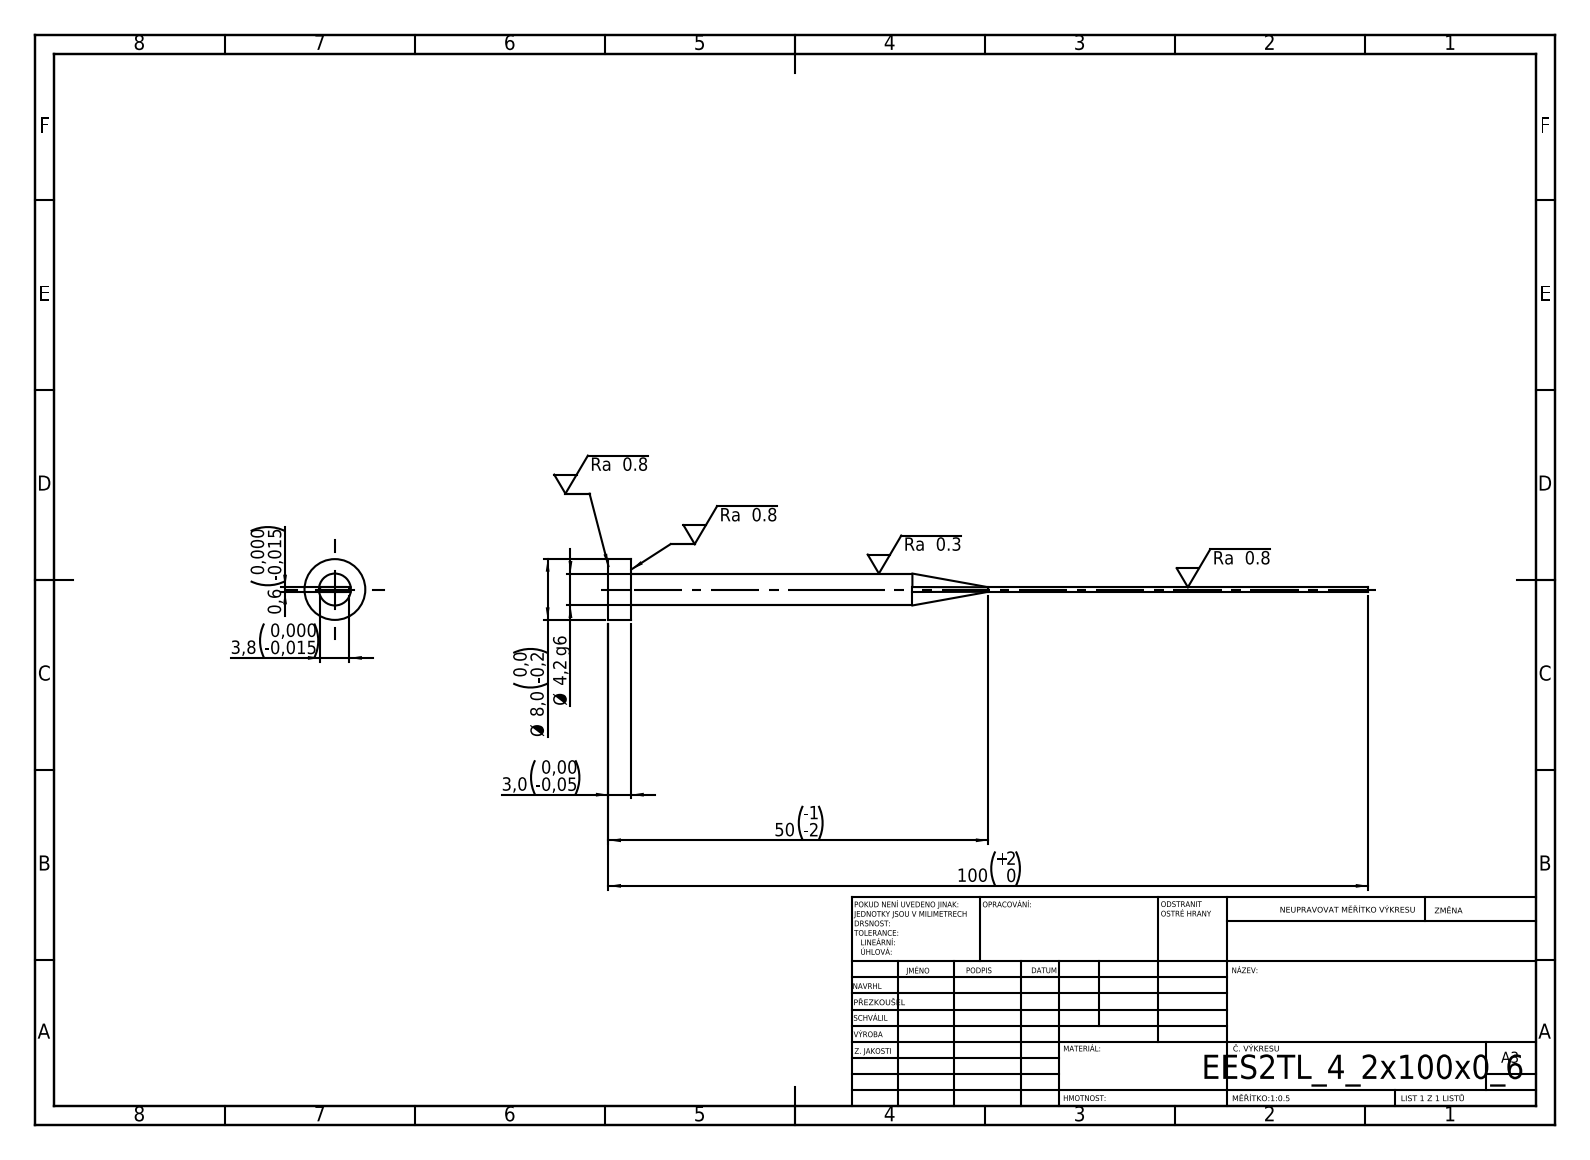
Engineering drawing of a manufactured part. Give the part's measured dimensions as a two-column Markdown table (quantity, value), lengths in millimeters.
| quantity | value |
| --- | --- |
| STEP written by | SolidWorks 2019 (CONFIG_CONTROL_DESIGN) |
| units | millimeters |
| bodies | 1 solid, 15 faces (7 planar, 4 cylindrical, 4 other) |
| overall size | 100 × 8 × 8 |
| volume | 853 mm³ |
| surface area | 1 198 mm² |
| round bosses / shafts (diameter × count) | 8 × 1, 4.2 × 1 |
| main face-to-face distances | 0.6, 3, 3.8, 100, 97 |
